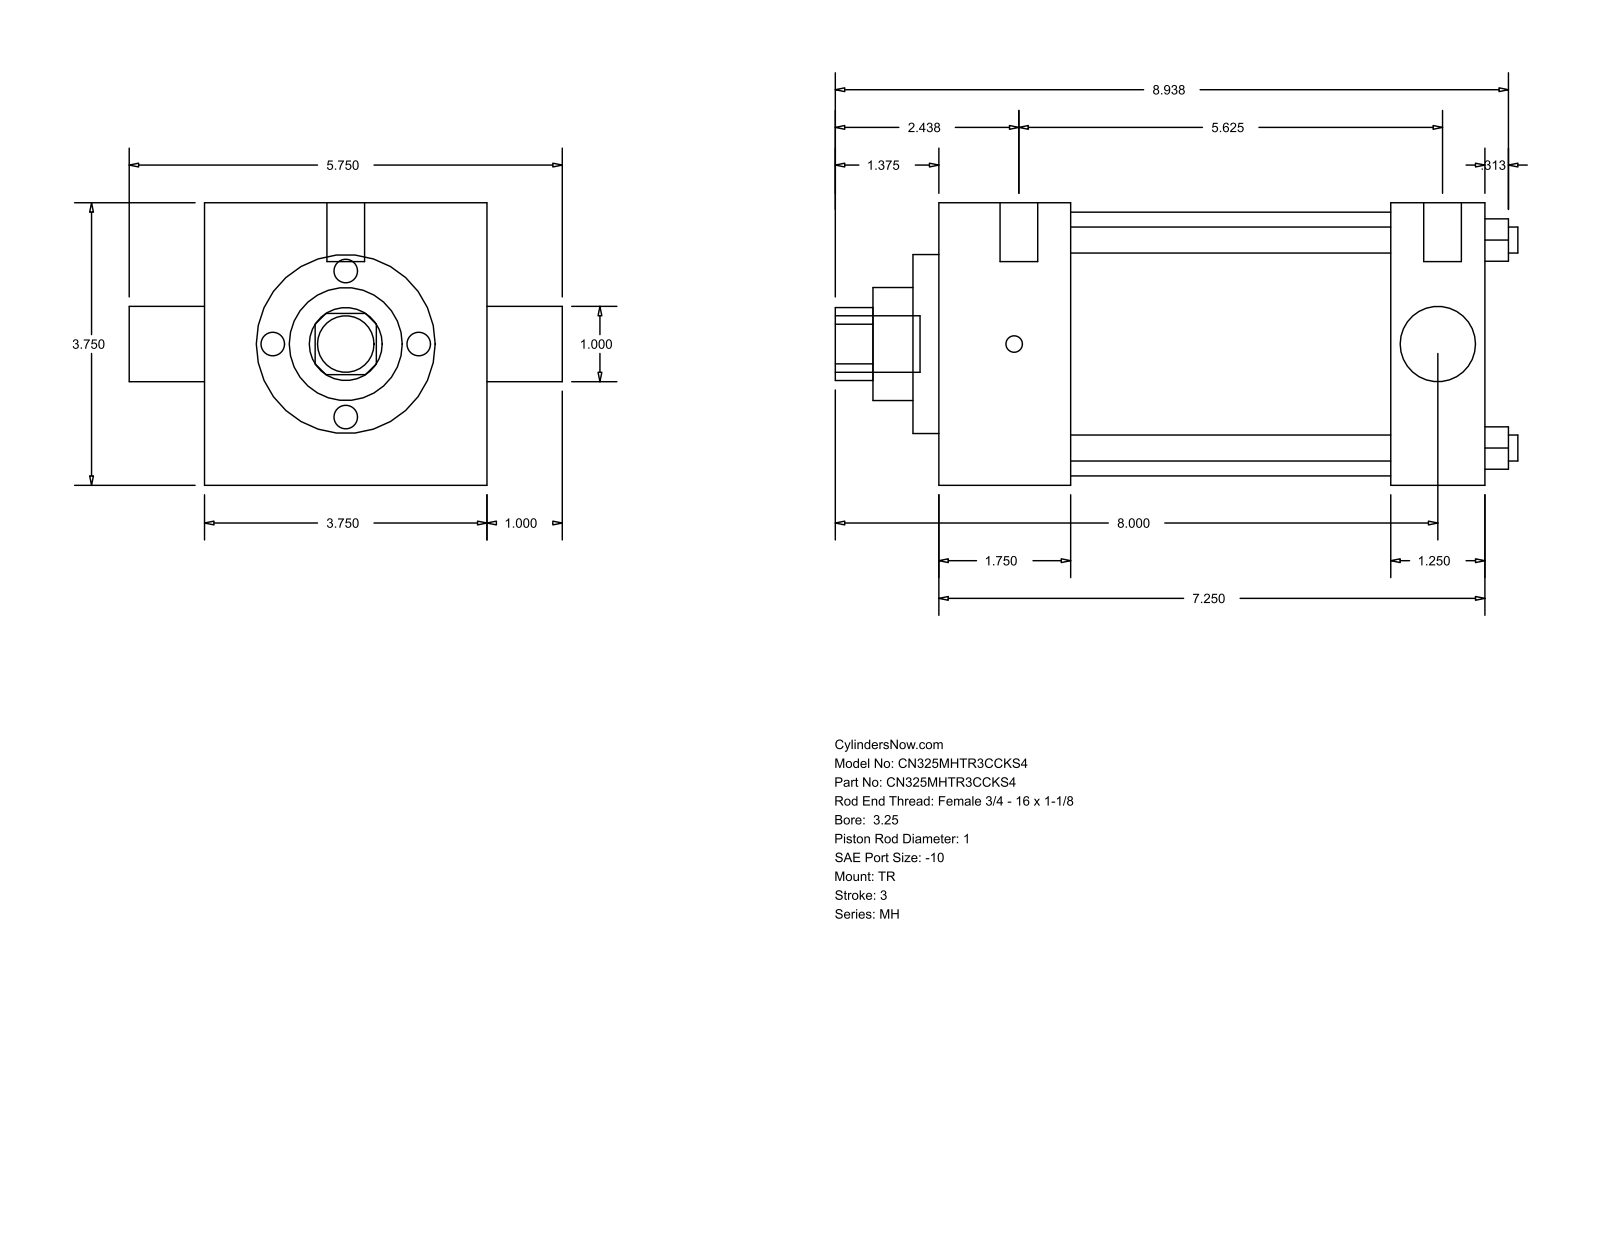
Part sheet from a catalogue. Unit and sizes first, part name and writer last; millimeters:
Units: millimetres
Overall size (bounding box): 230.19 × 146.05 × 95.25
Round holes (diameter × count): ⌀8.76 ×4, ⌀25.4 ×2, ⌀38.1 ×1, ⌀60.33 ×1, ⌀88.9 ×1
Round bosses / shafts (diameter × count): ⌀5.56 ×3, ⌀12.7 ×2, ⌀19.05 ×1
Partial cylindrical surfaces — rounded edges, fillets, slot ends (radius × count): R12.29 ×1
Main face-to-face distances: 95.24, 184.15, 44.46, 152.4, 107.94, 139.69, 31.75, 8.73, 53.19, 161.13
Hole centre spacings: 49.57, 70.1, 99.14
Bodies: 0 solids, 86 faces (61 planar, 25 cylindrical, 0 other)
Part name (STEP PRODUCT): MH_TR__0325_1
STEP written by: GSSL Pune (CONFIG_CONTROL_DESIGN)
